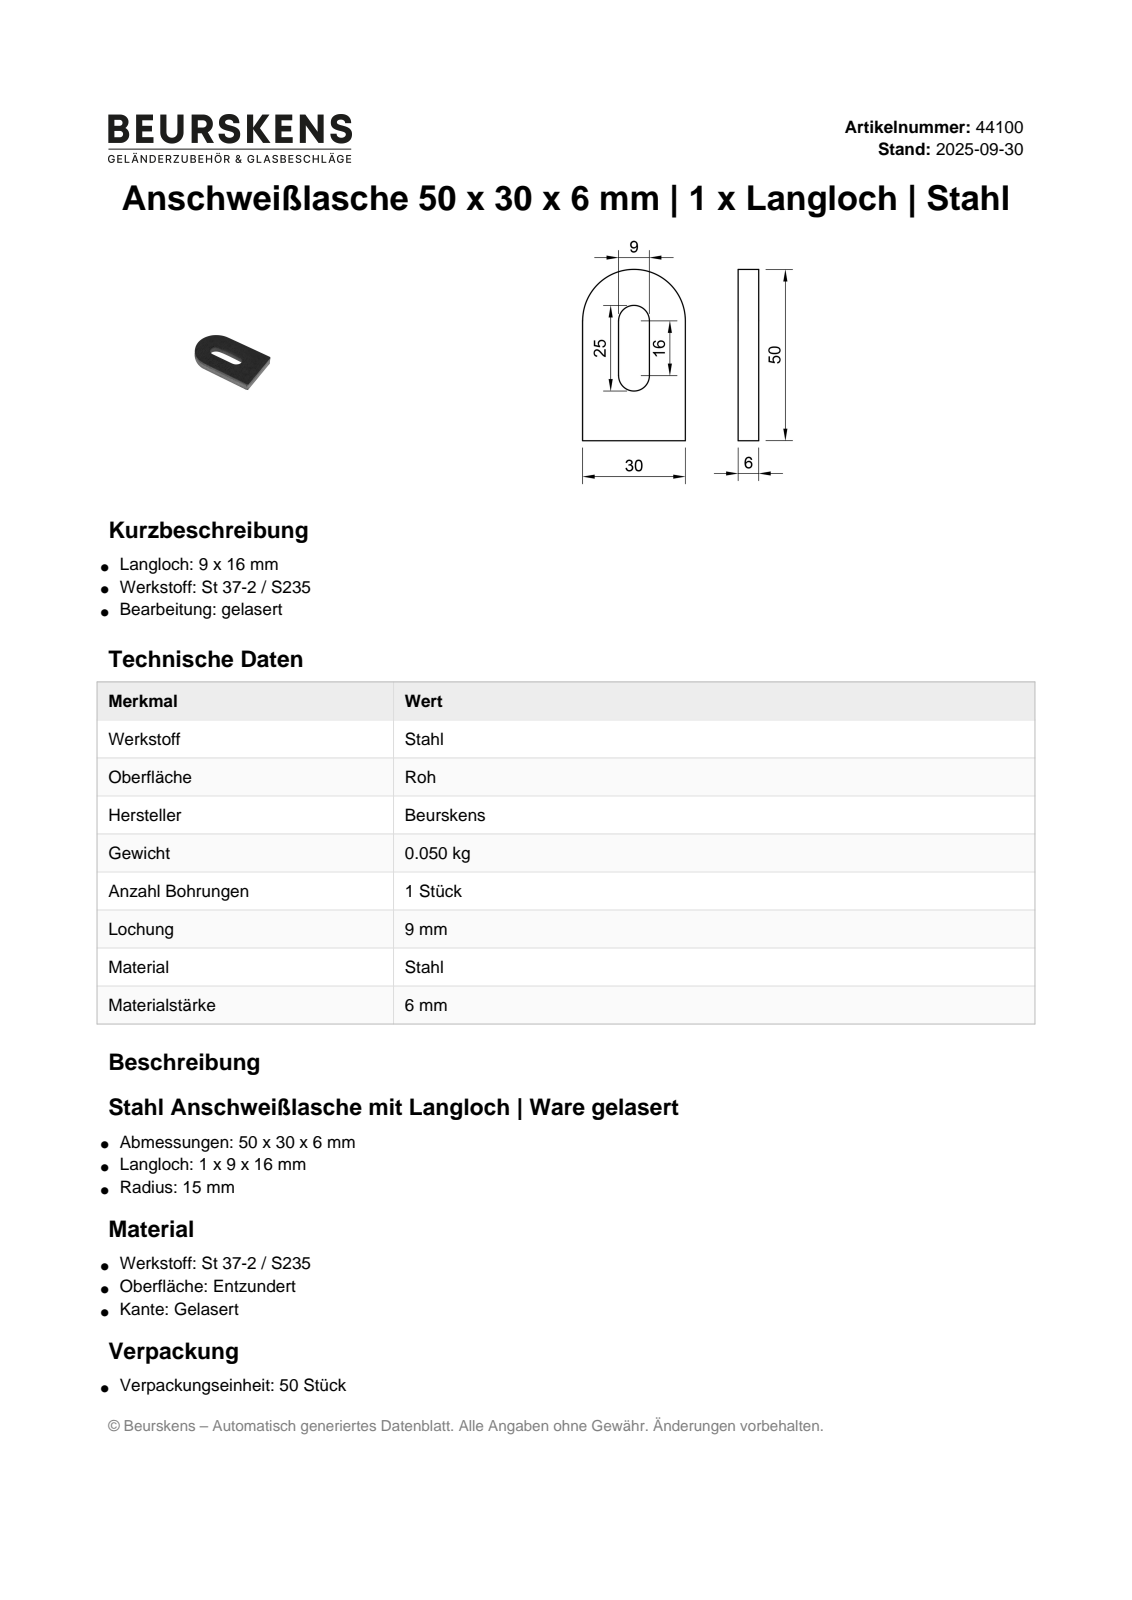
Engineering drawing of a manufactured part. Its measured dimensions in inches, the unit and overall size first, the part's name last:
Units: inches
Overall size (bounding box): 1.969 × 1.181 × 0.236
Partial cylindrical surfaces — rounded edges, fillets, slot ends (radius × count): R0.177 ×2, R0.591 ×1
Main face-to-face distances: 0.236, 1.181, 0.413, 0.768, 0.354
Volume: 0.438 in³ · Surface area: 5.636 in²
Bodies: 1 solid, 10 faces (7 planar, 3 cylindrical, 0 other)
Part name (STEP PRODUCT): 44100
STEP written by: Autodesk Inventor 2023 (AUTOMOTIVE_DESIGN)
